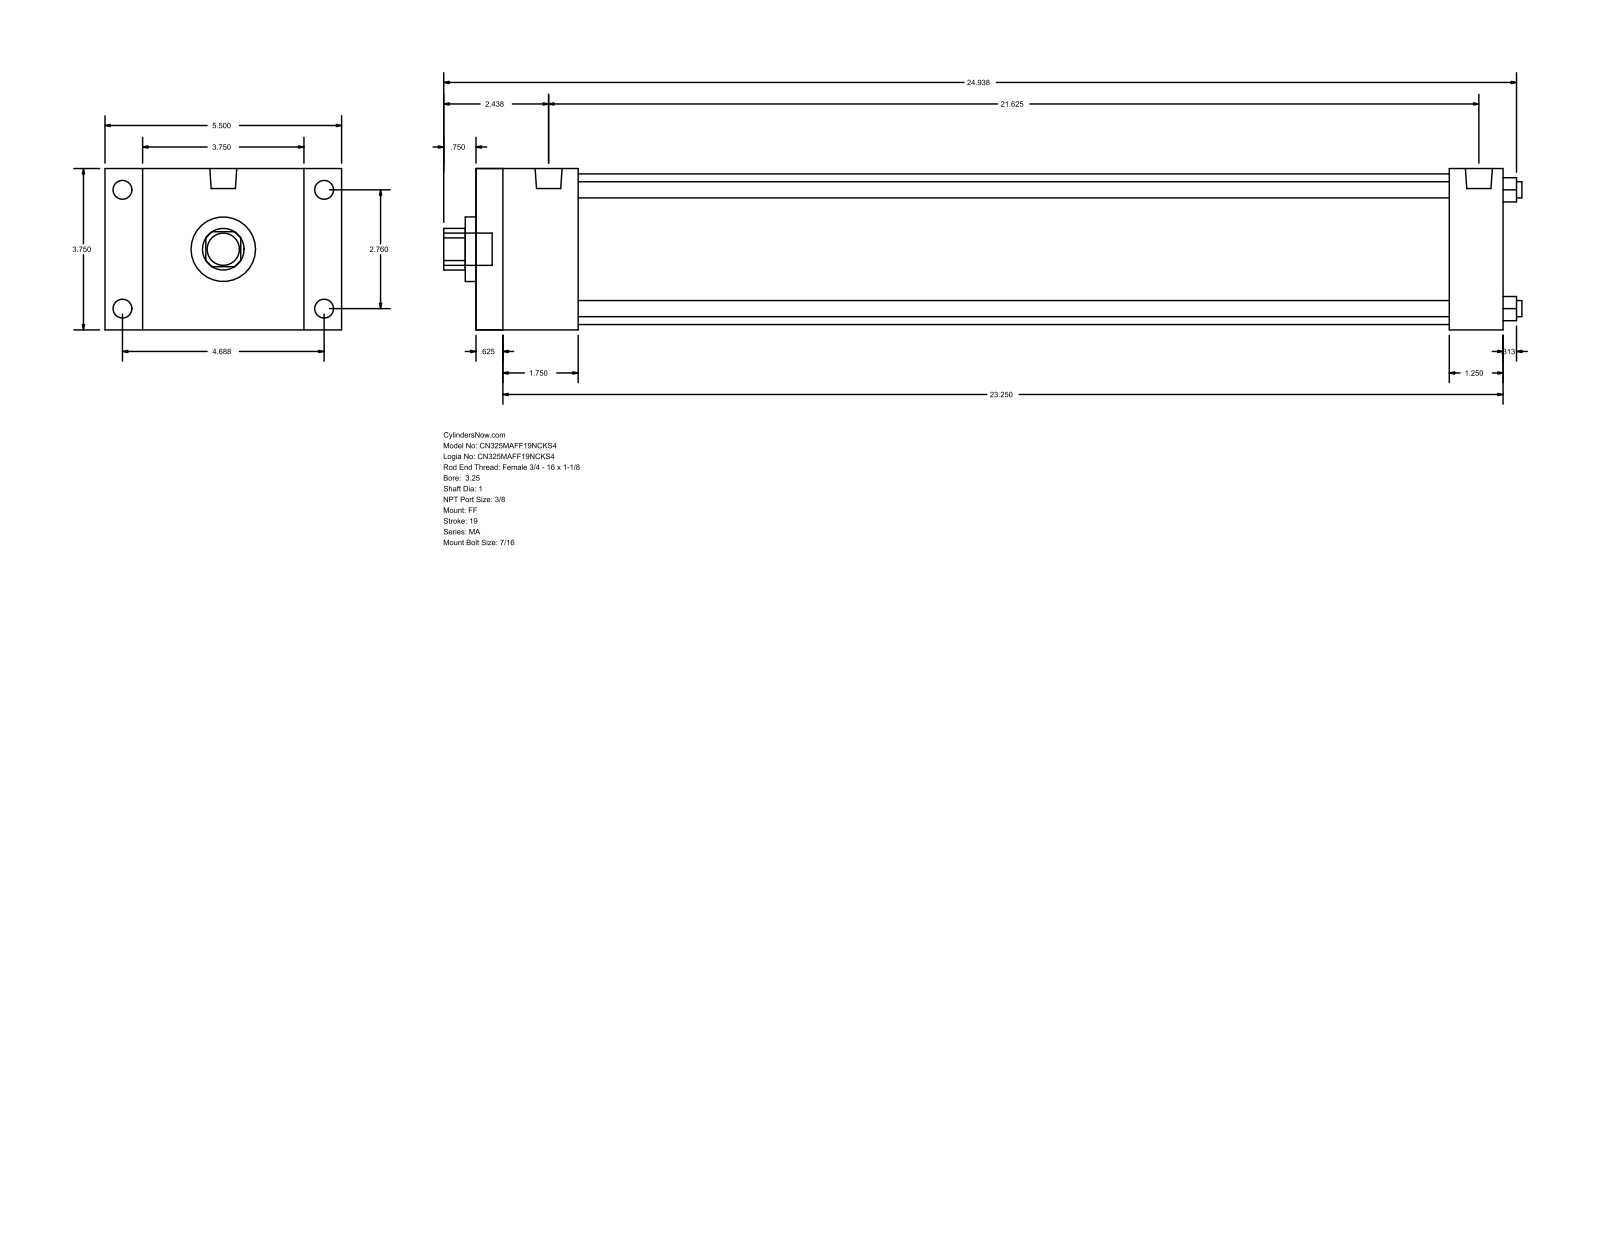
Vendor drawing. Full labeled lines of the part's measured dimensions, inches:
Part name (STEP PRODUCT): MA_FF__0325_1
STEP written by: GSSL Pune (CONFIG_CONTROL_DESIGN)
Units: inches
Bodies: 0 solids, 92 faces (64 planar, 28 cylindrical, 0 other)
Overall size (bounding box): 25.063 × 5.5 × 3.75
Round holes (diameter × count): ⌀0.375 ×4, ⌀1 ×1, ⌀1.5 ×1, ⌀3.5 ×1
Round bosses / shafts (diameter × count): ⌀0.437 ×8, ⌀0.627 ×2, ⌀0.75 ×1
Partial cylindrical surfaces — rounded edges, fillets, slot ends (radius × count): R0.484 ×1
Main face-to-face distances: 3.75, 23.875, 0.625, 23.25, 0.875, 4.625, 2.375, 22.625, 1.75, 22
Hole centre spacings: 1.952, 2.76, 3.903
